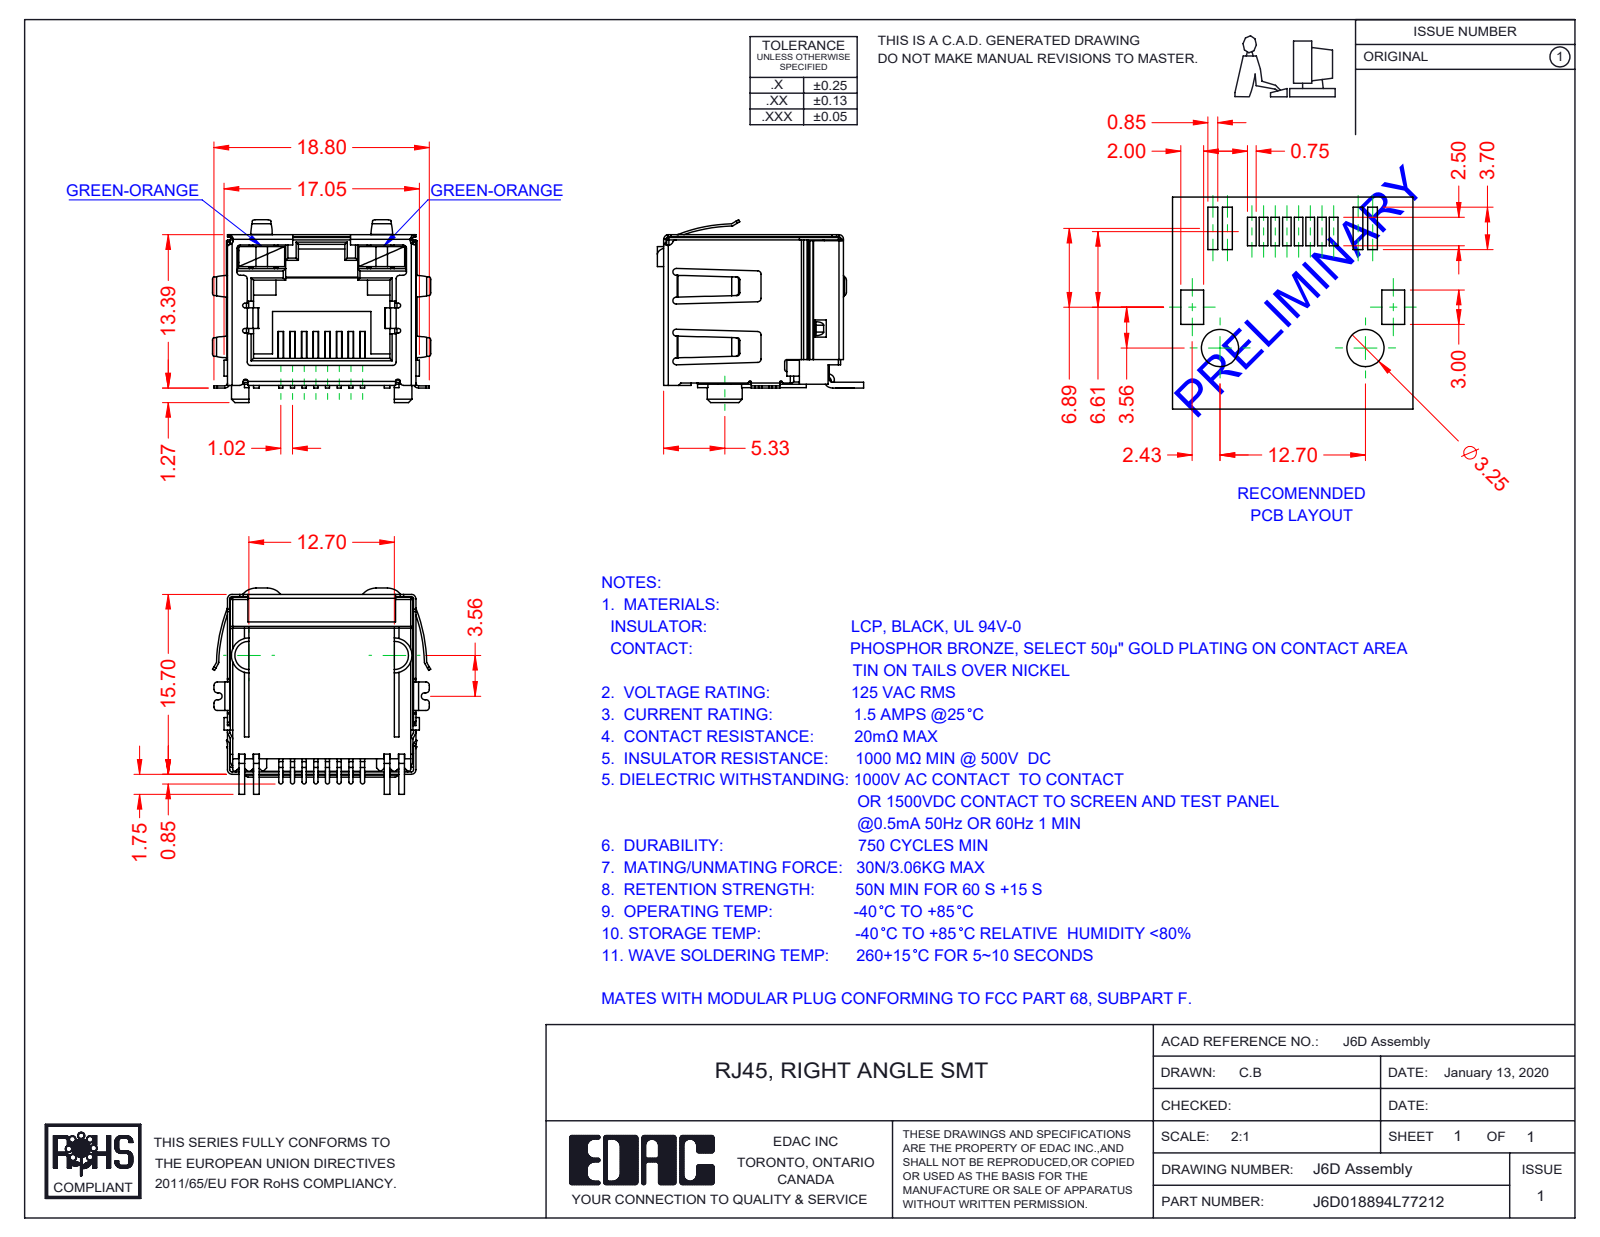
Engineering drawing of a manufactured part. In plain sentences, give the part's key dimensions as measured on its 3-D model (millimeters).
The part is named "6D Shield_LED - EMI; 6D LED LH_7-Green-Orange; 6D Insulator; 6D LED RH_7-Green-Orange (+2 more)". Its 3-D file was written by "SolidWorks 2016 (CONFIG_CONTROL_DESIGN)". It is 12 solids with 1034 faces: 703 planar, 286 cylindrical and 45 other. Overall it measures 19.06 by 18 by 15.95 millimeters. Its volume is 1 790 cubic millimeters and its surface area 4 796 square millimeters. Partial cylindrical surfaces (rounded edges, fillets, slot ends): 55 of radius 0.3, 40 of radius 0.2, 19 of radius 0.4, 16 of radius 0.25, 12 of radius 0.1, 8 of radius 0.15, 8 of radius 0.18, 6 of radius 0.5. The main face-to-face distances are 16, 16.2, 16.25, 2.25, 1, 15.95, 12.8, 0.45, 13.05, 10.6.
